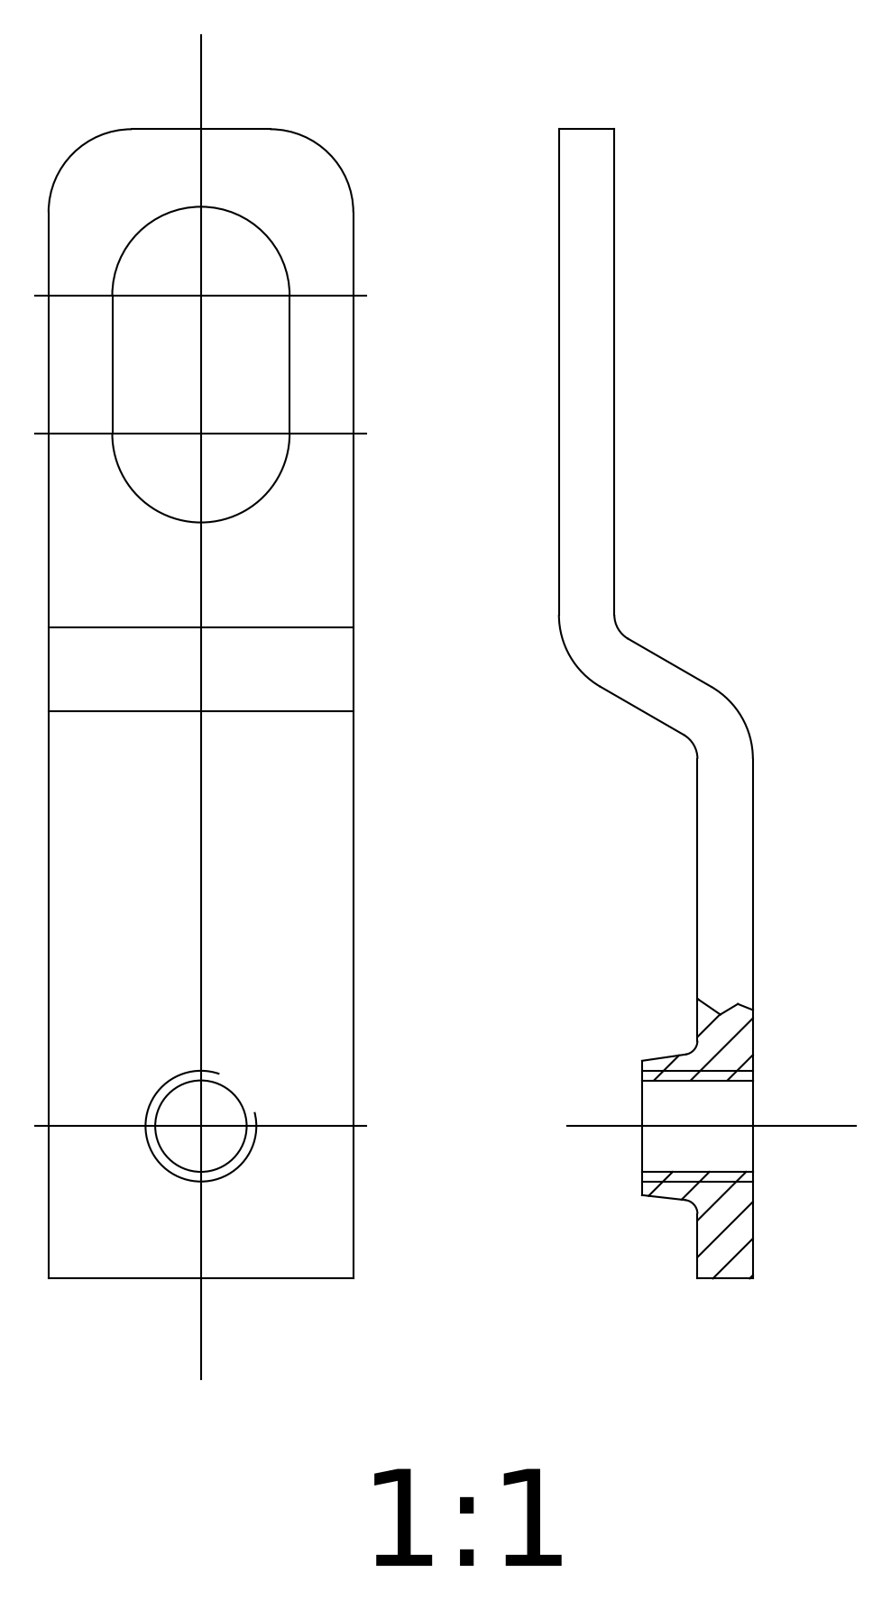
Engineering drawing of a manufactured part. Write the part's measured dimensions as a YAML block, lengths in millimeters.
part_name: "MR28540"
step_written_by: "SolidWorks 2009 (AUTOMOTIVE_DESIGN)"
units: millimeters
bodies: {solids: 1, faces: 30, planar: 13, cylindrical: 11, other: 6}
overall_size: [41.51, 11, 7]
volume: 849
surface_area: 1159
round_holes:
  - {diameter: 3.3, count: 1}
partial_cylinders:
  - {radius: 3, count: 4}
  - {radius: 1, count: 2}
  - {radius: 3.2, count: 2}
face_to_face_distances: [2, 5, 3, 7, 11, 2.3, 8.7, 1, 4, 41.51]
